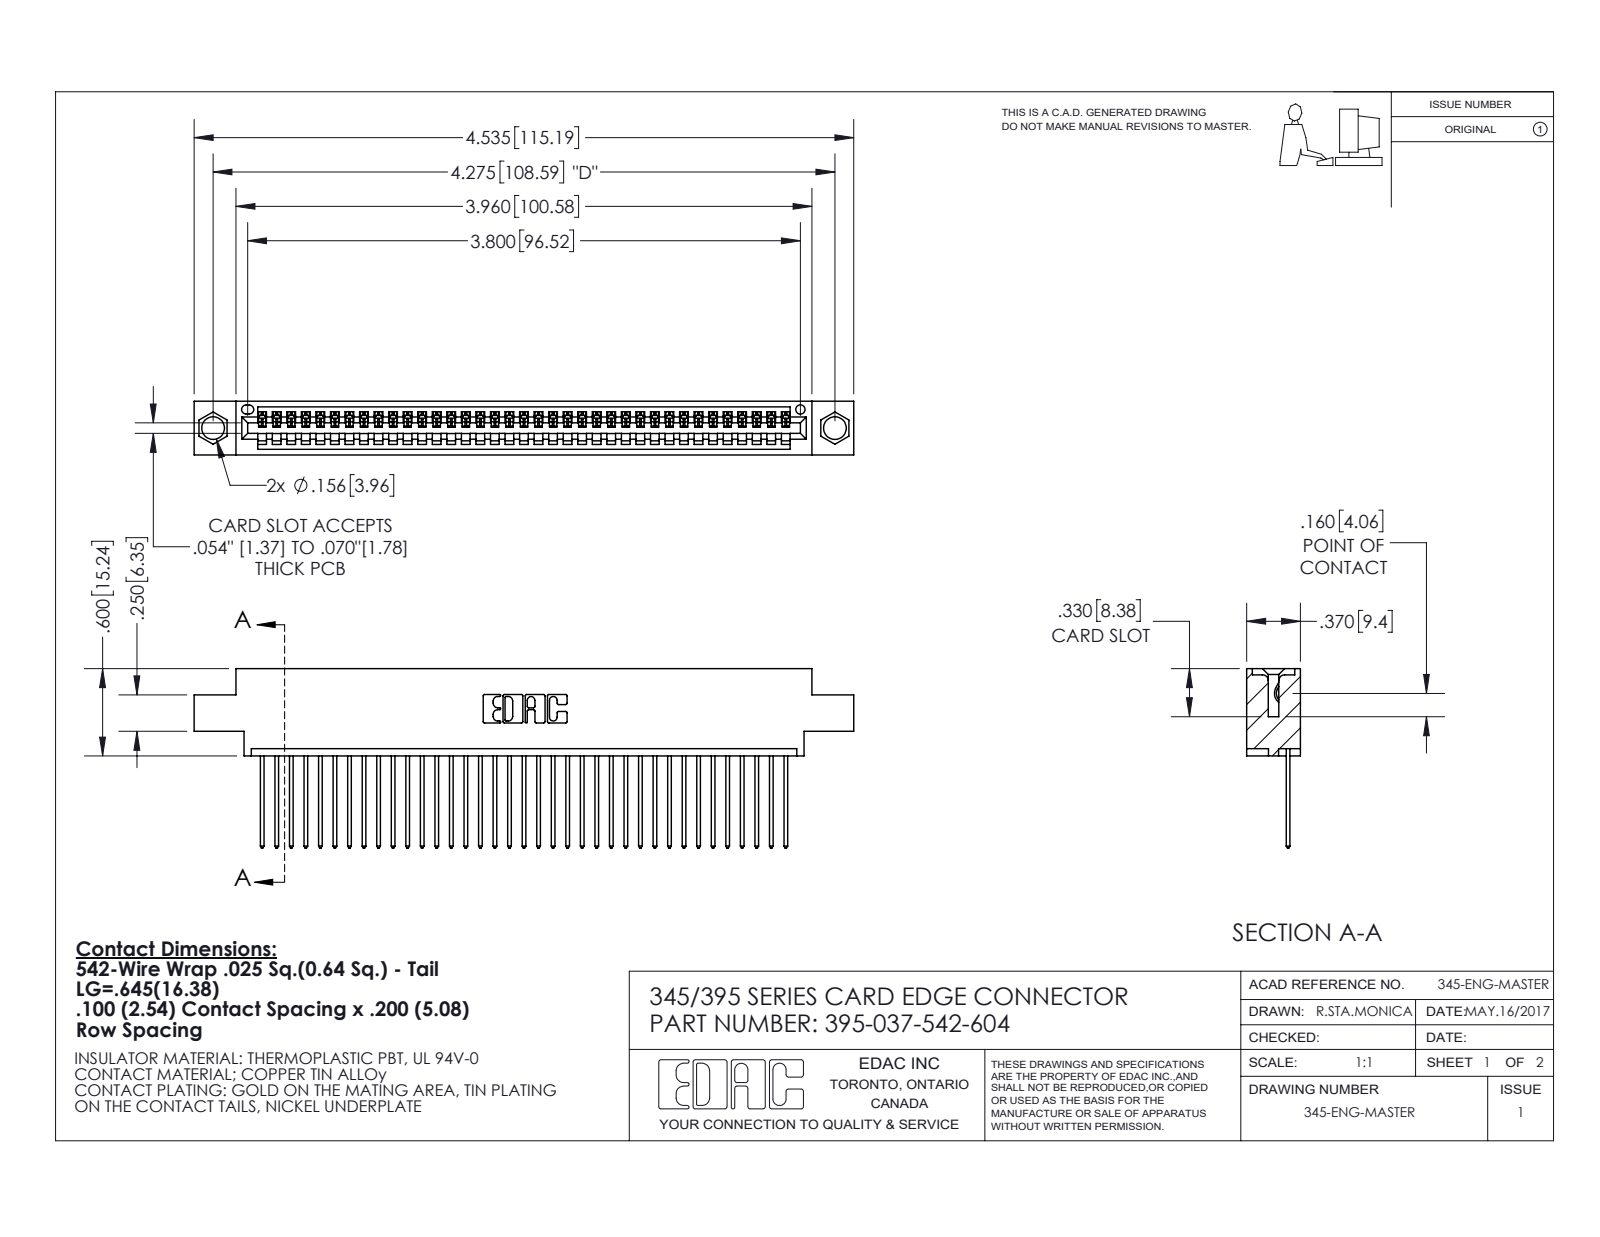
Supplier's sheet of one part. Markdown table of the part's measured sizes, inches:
| quantity | value |
| --- | --- |
| part name | 345 Part_0.170 Offset - 0.156 Dia-TI; 395-037-542-604; 345-292-001_345-293-142 |
| STEP written by | SolidWorks 2020 (CONFIG_CONTROL_DESIGN) |
| units | inches |
| bodies | 38 solids, 2290 faces (1578 planar, 712 cylindrical, 0 other) |
| overall size | 4.535 × 1.232 × 0.37 |
| volume | 0.657 in³ |
| surface area | 22.82 in² |
| round holes (diameter × count) | 0.156 × 2, 0.064 × 1 |
| partial cylindrical surfaces (radius × count) | 0.006 × 74, 0.01 × 74, 0.01 × 22, 0.007 × 6, 0.031 × 6, 0.026 × 3, 0.031 × 2, 0.04 × 2 |
| main face-to-face distances | 0.072, 0.298, 0.37, 0.098, 0.272, 0.025, 0.2, 0.225, 0.175, 0.149 |
| hole center spacings | 0.27, 4.039, 4.275 |
